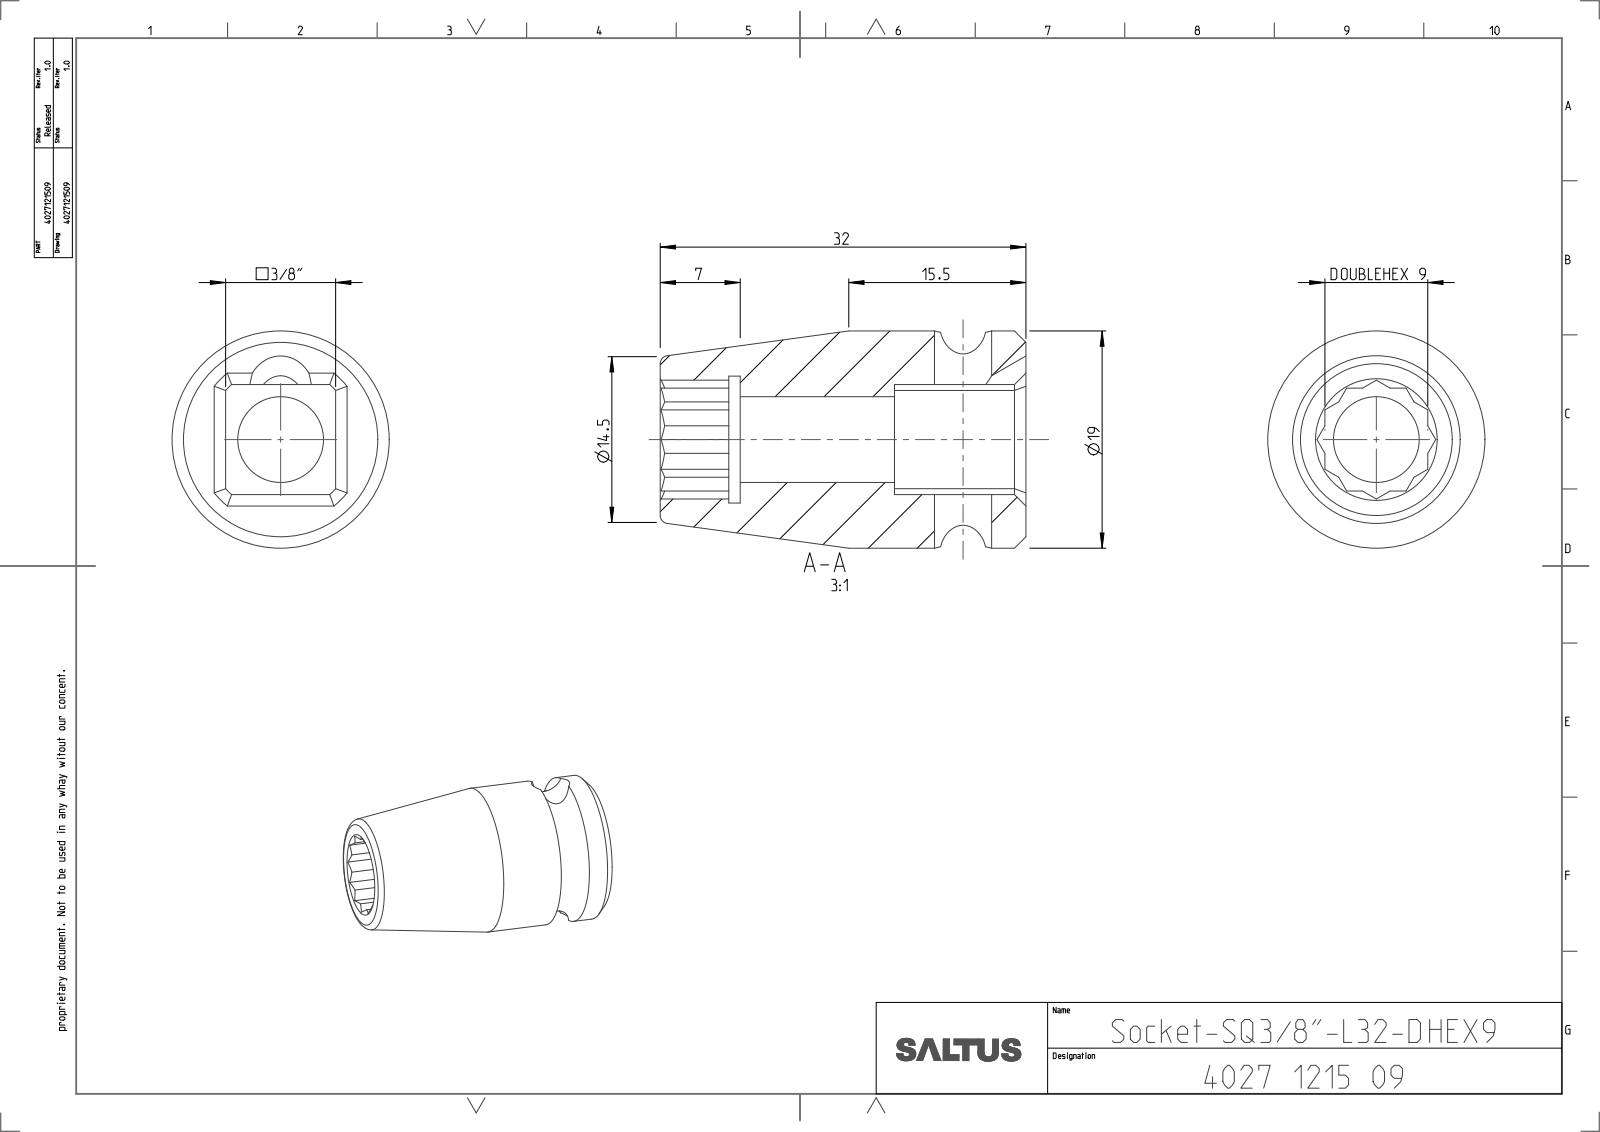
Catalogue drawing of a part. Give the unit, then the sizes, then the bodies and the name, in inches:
Units: inches
Overall size (bounding box): 1.26 × 0.748 × 0.748
Round holes (diameter × count): ⌀0.197 ×1, ⌀0.295 ×1, ⌀0.437 ×1
Round bosses / shafts (diameter × count): ⌀0.748 ×1
Partial cylindrical surfaces — rounded edges, fillets, slot ends (radius × count): R0.118 ×1, R0.254 ×1
Main face-to-face distances: 0.379, 0.354, 0.012, 0.367, 0.984, 1.26, 0.276, 0.453, 0.531, 0.807
Volume: 0.328 in³ · Surface area: 4.958 in²
Bodies: 1 solid, 69 faces (38 planar, 17 cylindrical, 14 other)
Part name (STEP PRODUCT): 4027121509
STEP written by: CREO PARAMETRIC BY PTC INC, 2022414 (CONFIG_CONTROL_DESIGN)
